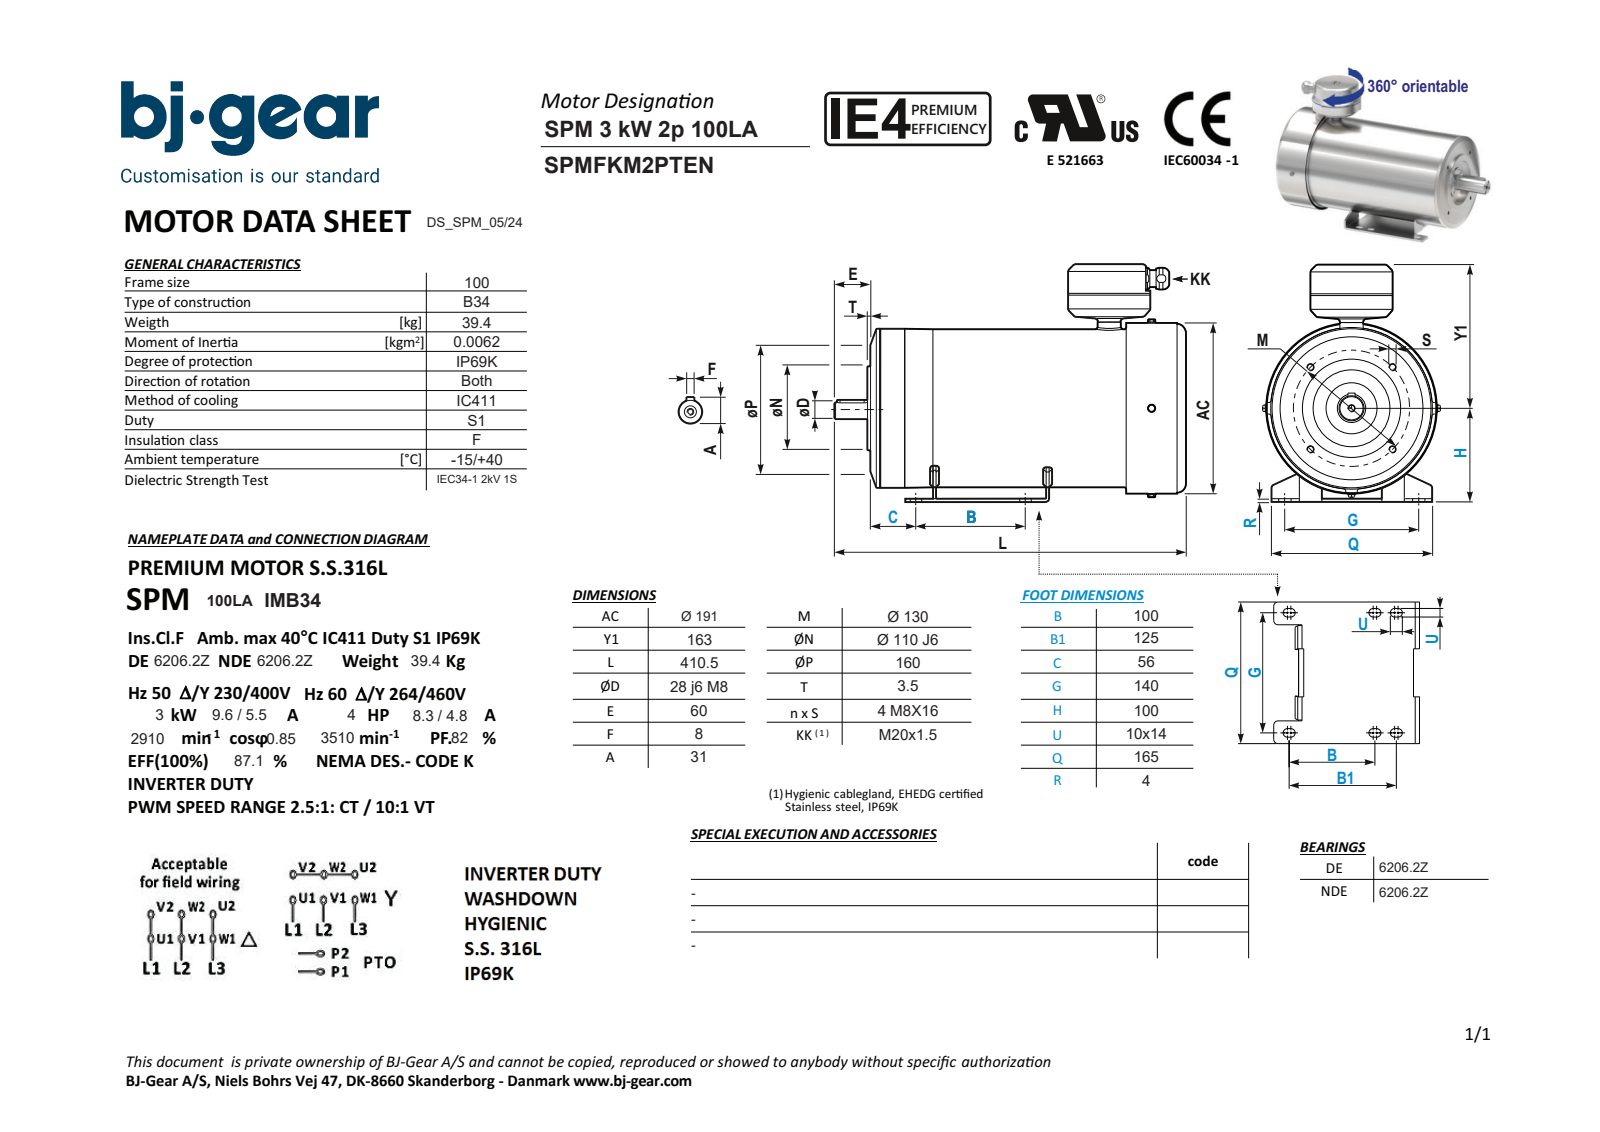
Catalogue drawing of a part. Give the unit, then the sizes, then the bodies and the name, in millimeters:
Units: millimetres
Overall size (bounding box): 410.5 × 262 × 199
Round holes (diameter × count): ⌀6.65 ×4, ⌀4.92 ×1, ⌀7 ×1, ⌀8.4 ×1, ⌀13.4 ×1, ⌀16 ×1, ⌀85 ×1
Round bosses / shafts (diameter × count): ⌀9 ×2, ⌀191 ×1, ⌀178 ×1, ⌀177.98 ×1, ⌀110 ×1, ⌀93 ×1, ⌀84 ×1, ⌀30 ×1
Partial cylindrical surfaces — rounded edges, fillets, slot ends (radius × count): R5 ×18, R3 ×6, R1 ×4, R4 ×4, R12.8 ×1, R88.5 ×1
Main face-to-face distances: 4, 350.5, 6, 344.5, 262, 258, 67, 3, 277.5, 283.5
Hole centre spacings: 65, 91.92, 110.55, 129.99, 197.87, 146.5
Volume: 9 457 000 mm³ · Surface area: 350 638 mm²
Bodies: 2 solids, 288 faces (121 planar, 103 cylindrical, 64 other)
Part name (STEP PRODUCT): SPMFKM2PTEVN4KFU1-N---NNN; SPMFKM2JTEVN4KFU1-N---NNN; SPM909022
STEP written by: Solid Edge (AUTOMOTIVE_DESIGN)
